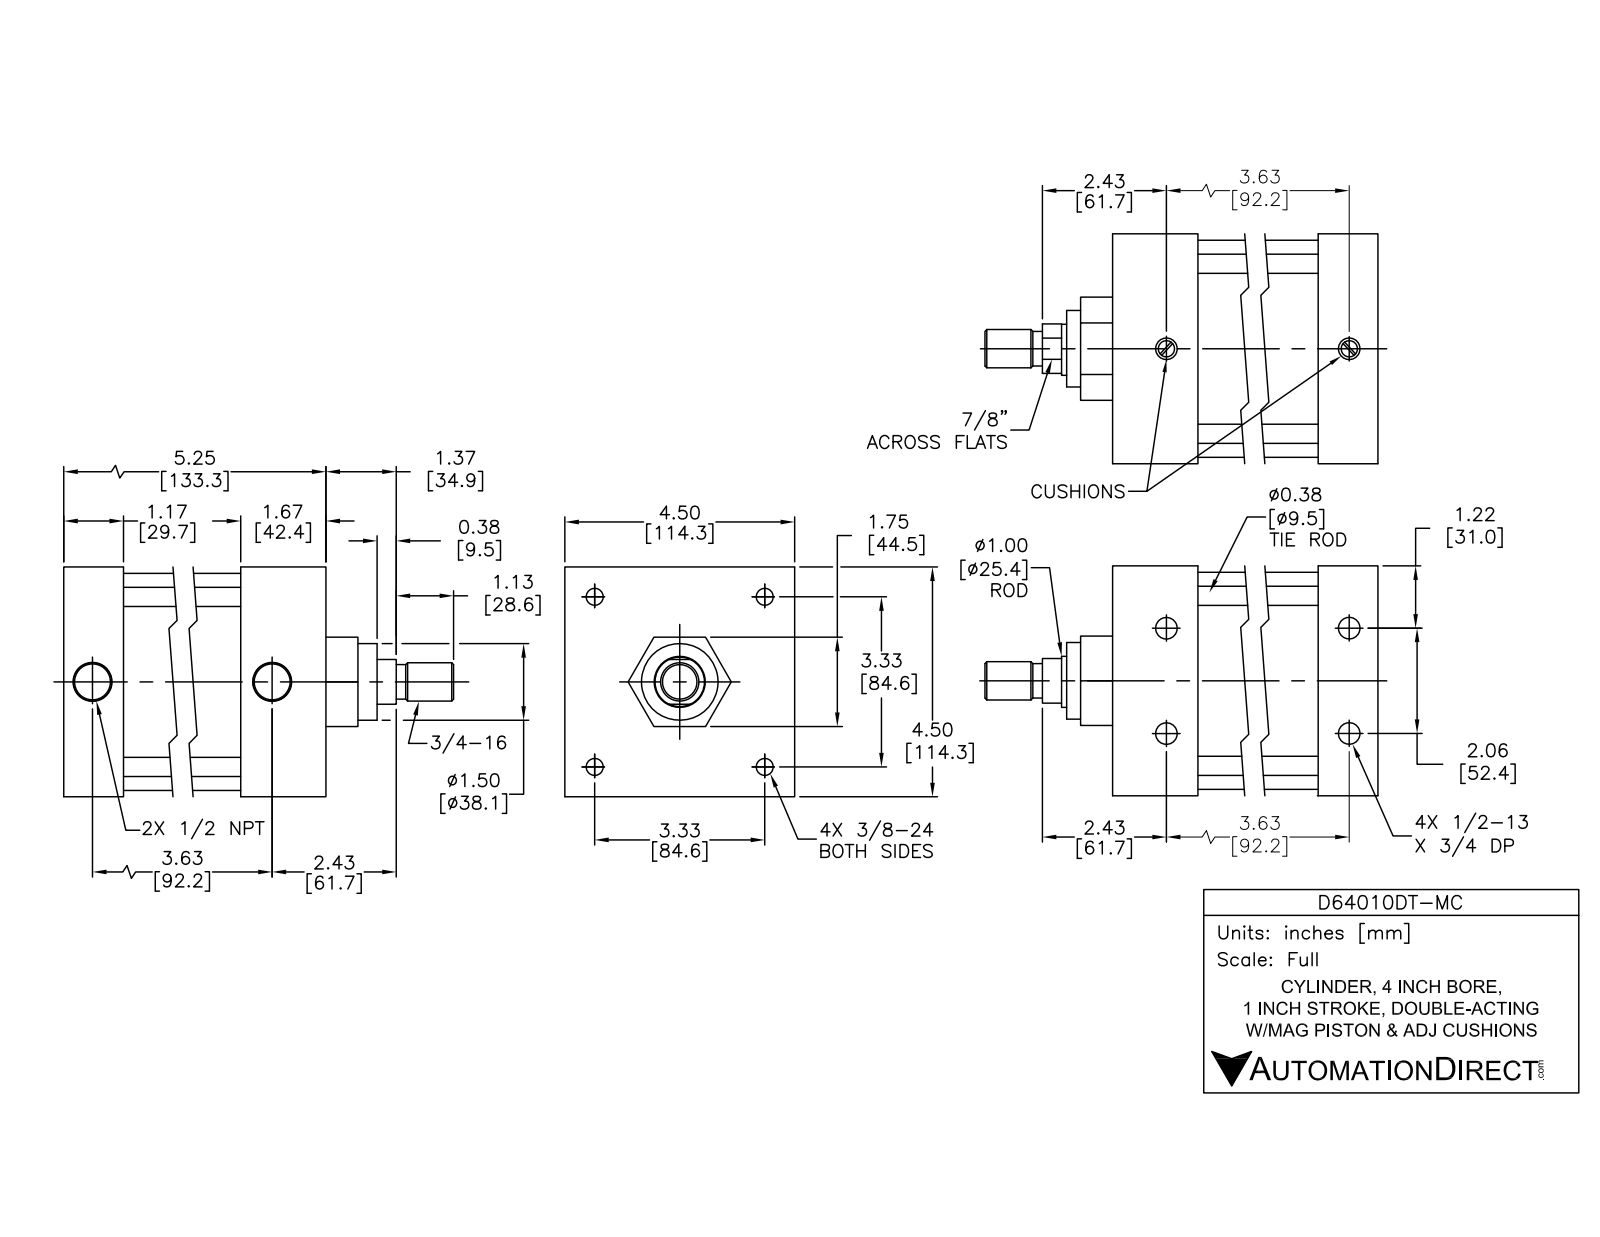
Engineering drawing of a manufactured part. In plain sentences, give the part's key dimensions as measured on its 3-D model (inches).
The part is named "D64010DT-M PISTON; D64010DT-MC; D64010DT-M BODY". Its 3-D file was written by "SolidWorks 2015 (AUTOMOTIVE_DESIGN)". It is 12 solids with 303 faces: 99 planar, 114 cylindrical and 90 other. Overall it measures 7.745 by 4.5 by 4.5 inches. Its volume is 80.11 cubic inches and its surface area 323.7 square inches. Round holes: 4 of diameter 0.33, 4 of diameter 0.406, 4 of diameter 0.417, 4 of diameter 0.625, 2 of diameter 0.5, 2 of diameter 0.766, 1 of diameter 1, 1 of diameter 1.003, 1 of diameter 4. Round bosses or shafts: 4 of diameter 0.609, 4 of diameter 0.375, 4 of diameter 0.34, 1 of diameter 4.25, 1 of diameter 3.997, 1 of diameter 1.75, 1 of diameter 0.997, 1 of diameter 0.97. Partial cylindrical surfaces (rounded edges, fillets, slot ends): 4 of radius 0.45. The main face-to-face distances are 4.5, 0.08, 2.326, 5.246, 1.75, 3.997, 1.249, 2.751, 1.246, 2.495. The hole center spacings are 1.031, 2.349, 3.322, 3.766, 3.622, 2.062, 4.168, 4.698.
